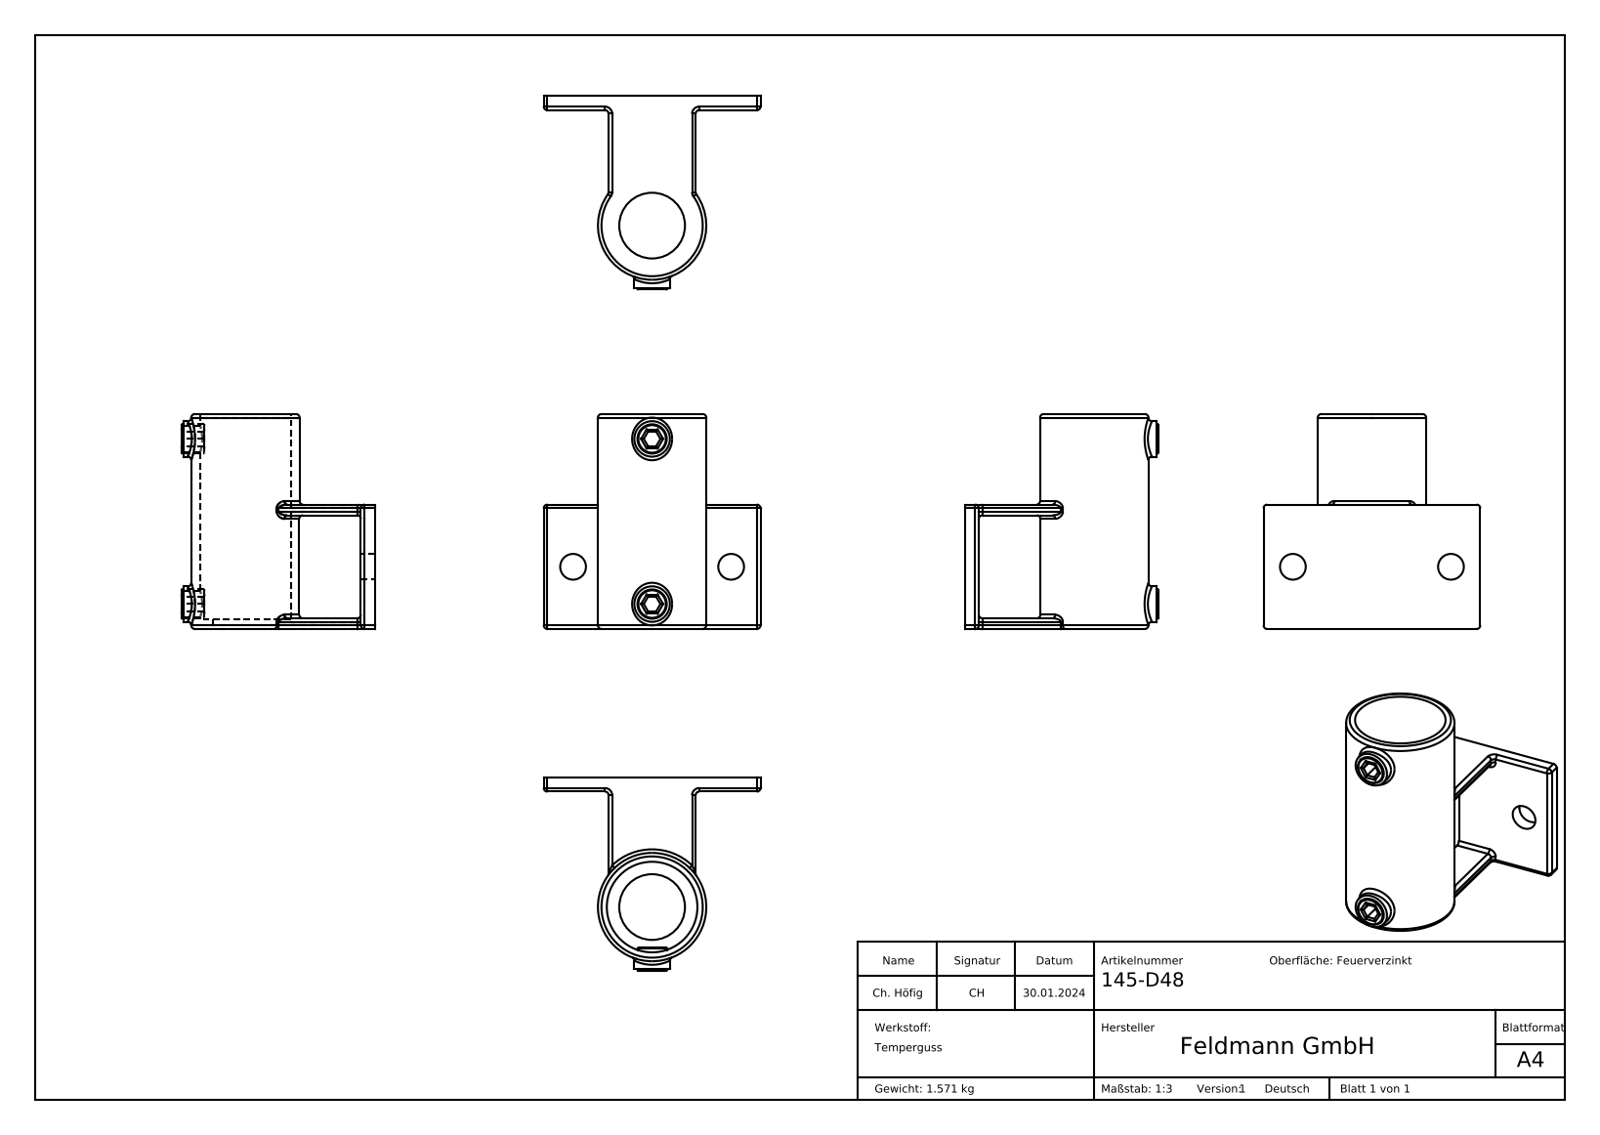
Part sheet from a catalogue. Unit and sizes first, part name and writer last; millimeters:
Units: millimetres
Overall size (bounding box): 122 × 121 × 109
Round holes (diameter × count): ⌀14.5 ×2, ⌀15.25 ×2, ⌀37 ×1, ⌀51 ×1
Round bosses / shafts (diameter × count): ⌀20 ×2, ⌀16.5 ×2, ⌀61 ×1
Partial cylindrical surfaces — rounded edges, fillets, slot ends (radius × count): R2 ×46
Main face-to-face distances: 8, 6, 64, 70, 58, 5.5, 0.5, 58.5, 64.5, 121
Hole centre spacings: 49.21, 84.64, 89, 93
Volume: 214 912 mm³ · Surface area: 78 856 mm²
Bodies: 3 solids, 135 faces (37 planar, 65 cylindrical, 33 other)
Part name (STEP PRODUCT): 145-D48 Teil1_145-D48 Teil1; 145-D48; 145-D48 Teil2_145-D48 Teil2
STEP written by: SolidWorks 2018 (CONFIG_CONTROL_DESIGN)
